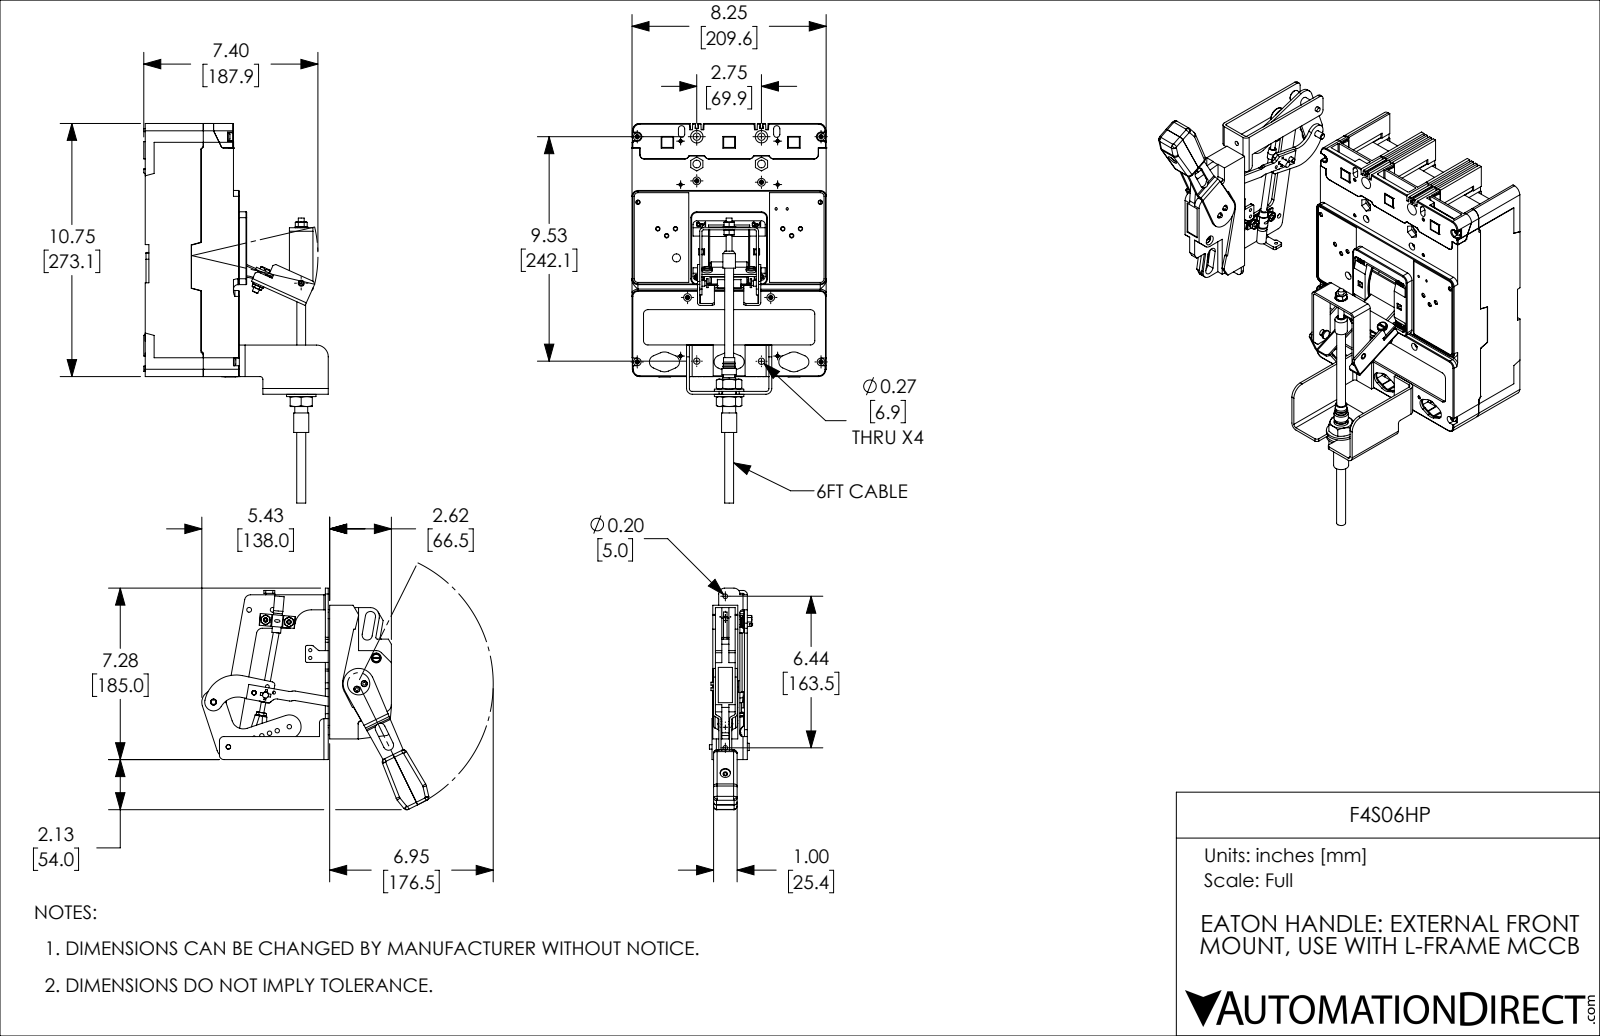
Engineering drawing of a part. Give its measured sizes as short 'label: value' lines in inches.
name: F4S06HP_HANDLE; F4S06HP; F4S06HP_BREAKER
written by: SolidWorks 2019 (CONFIG_CONTROL_DESIGN)
unit: in
bodies: 97 solids, 5868 faces (4033 planar, 1439 cylindrical, 396 other)
size: 16.357 × 14.407 × 9.651
volume: 239.3 in³; area: 1 189 in²
holes: 13× ⌀0.188, 10× ⌀0.17, 8× ⌀0.147, 7× ⌀0.328, 6× ⌀0.11, 6× ⌀0.14, 6× ⌀0.19, 6× ⌀0.203, 6× ⌀0.531, 4× ⌀0.146, 4× ⌀0.218, 4× ⌀0.25
bosses: 11× ⌀0.25, 6× ⌀0.375, 6× ⌀0.29, 4× ⌀0.5, 3× ⌀0.328, 3× ⌀0.312, 2× ⌀0.469, 2× ⌀0.425
rounds: 70× R0.062, 53× R0.032, 52× R0.25, 40× R0.125, 32× R0.03, 30× R0.188, 28× R0.06, 18× R0.156
face distances: 2.437, 8.25, 0.25, 3.718, 1.281, 0.125, 2.75, 0.094, 3.968, 1.531
hole spacings: 5.281, 2.75, 7.813, 5.282, 9.563, 2.532, 9.565, 2.531
